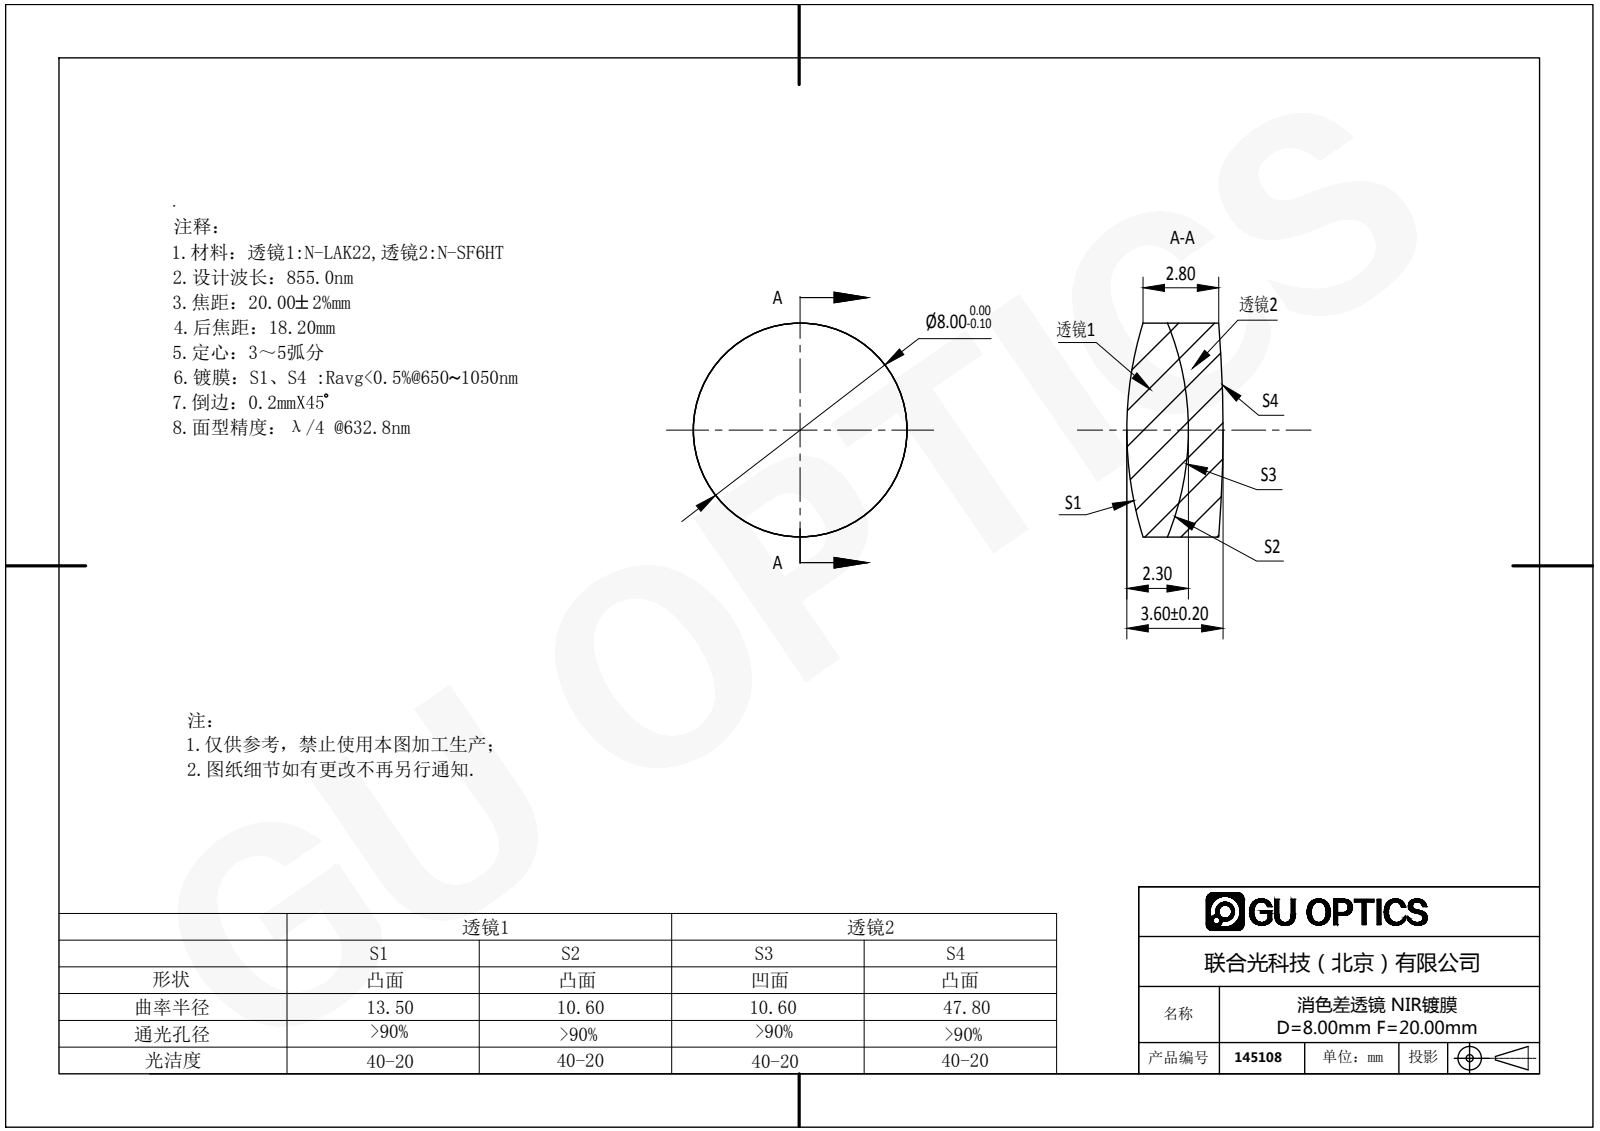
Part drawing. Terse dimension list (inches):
name: 145108
written by: SolidWorks 2016 (AUTOMOTIVE_DESIGN)
unit: in
bodies: 2 solids, 12 faces (0 planar, 4 cylindrical, 8 other)
size: 0.315 × 0.315 × 0.142
volume: 0.01 in³; area: 0.429 in²
bosses: 1× ⌀0.315
